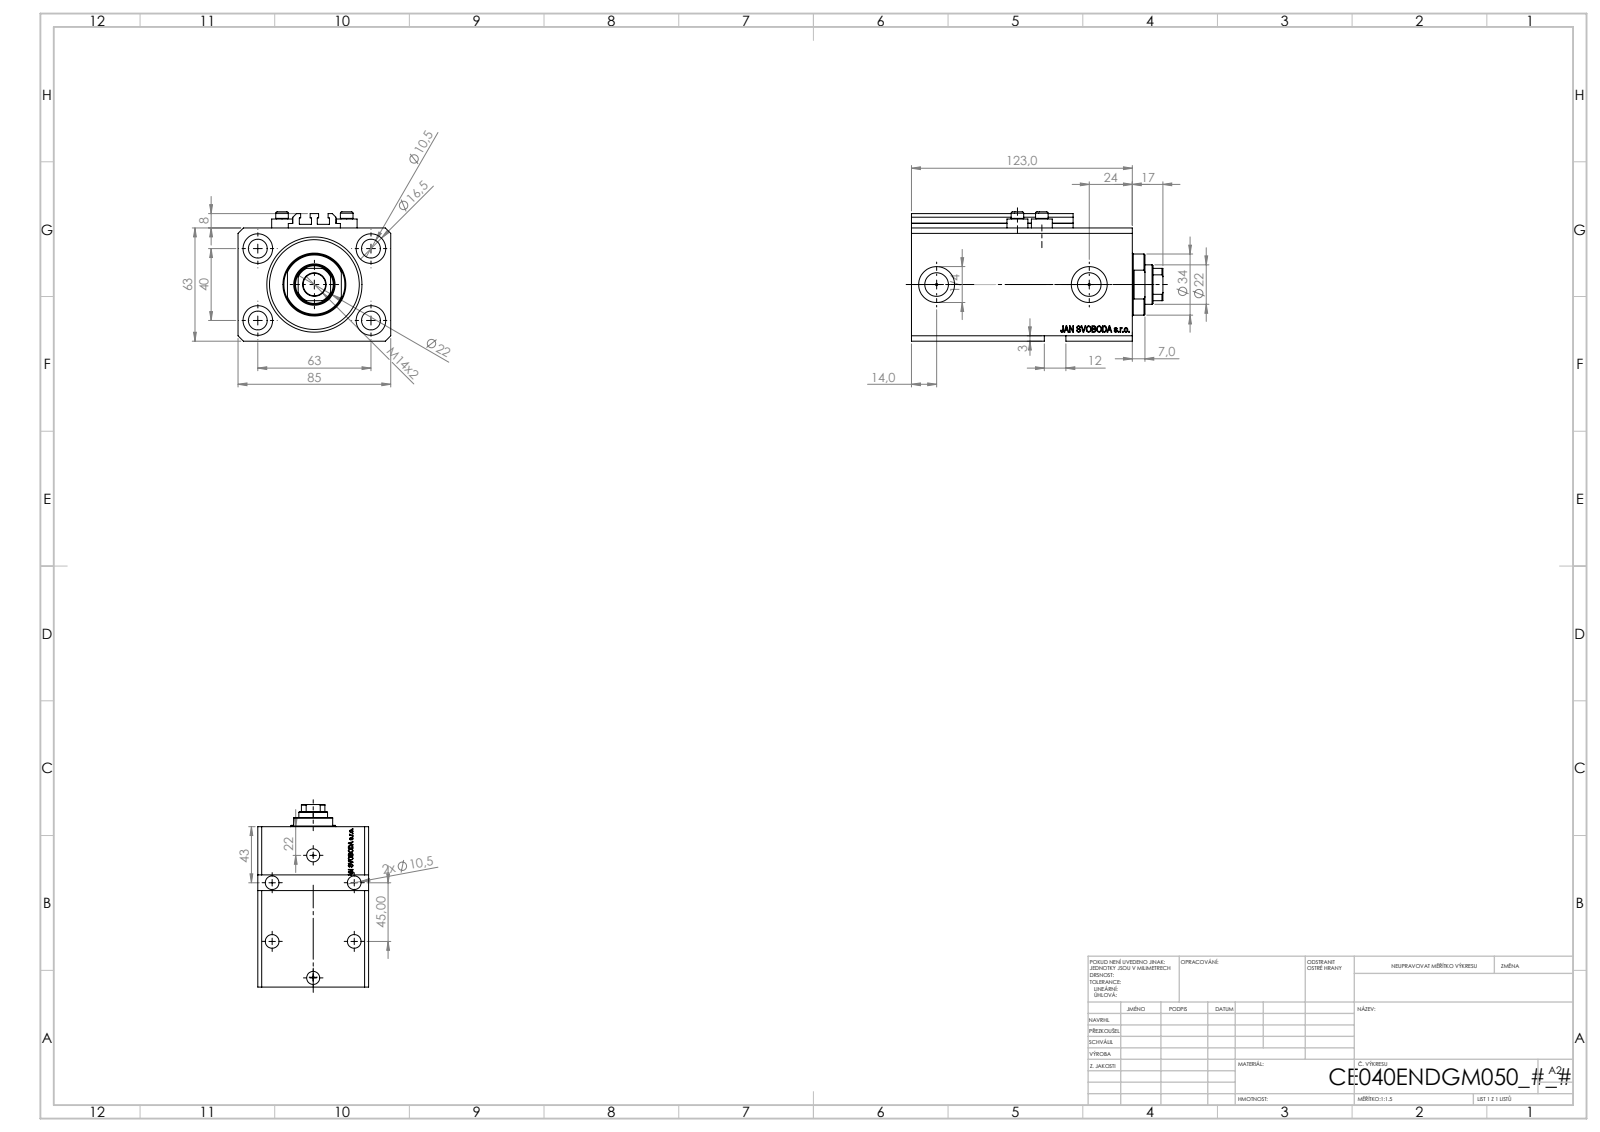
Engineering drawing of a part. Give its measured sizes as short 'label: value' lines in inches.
name: V250CE_E_Body; ALLEN BOLT V250CE; V250CE_C_VCP; V250CE_VC_E
written by: SolidWorks 2019 (CONFIG_CONTROL_DESIGN)
unit: in
bodies: 8 solids, 1123 faces (539 planar, 158 cylindrical, 426 other)
size: 5.512 × 3.346 × 2.835
volume: 33.75 in³; area: 186.8 in²
holes: 8× ⌀0.413, 4× ⌀0.049, 4× ⌀0.157, 4× ⌀0.65, 2× ⌀0.394, 2× ⌀0.518, 2× ⌀0.787, 1× ⌀0.492, 1× ⌀0.866, 1× ⌀1.575, 1× ⌀2.087
bosses: 4× ⌀0.457, 4× ⌀0.276, 1× ⌀1.339
rounds: 10× R0.008, 1× R0.413
face distances: 2.48, 3.346, 4.843, 0.669, 4.173, 0.449, 3.724, 4.394, 0.118, 2.205
hole spacings: 1.469, 2.48, 0.535, 0.606, 0.983, 1.084, 1.324, 1.417
